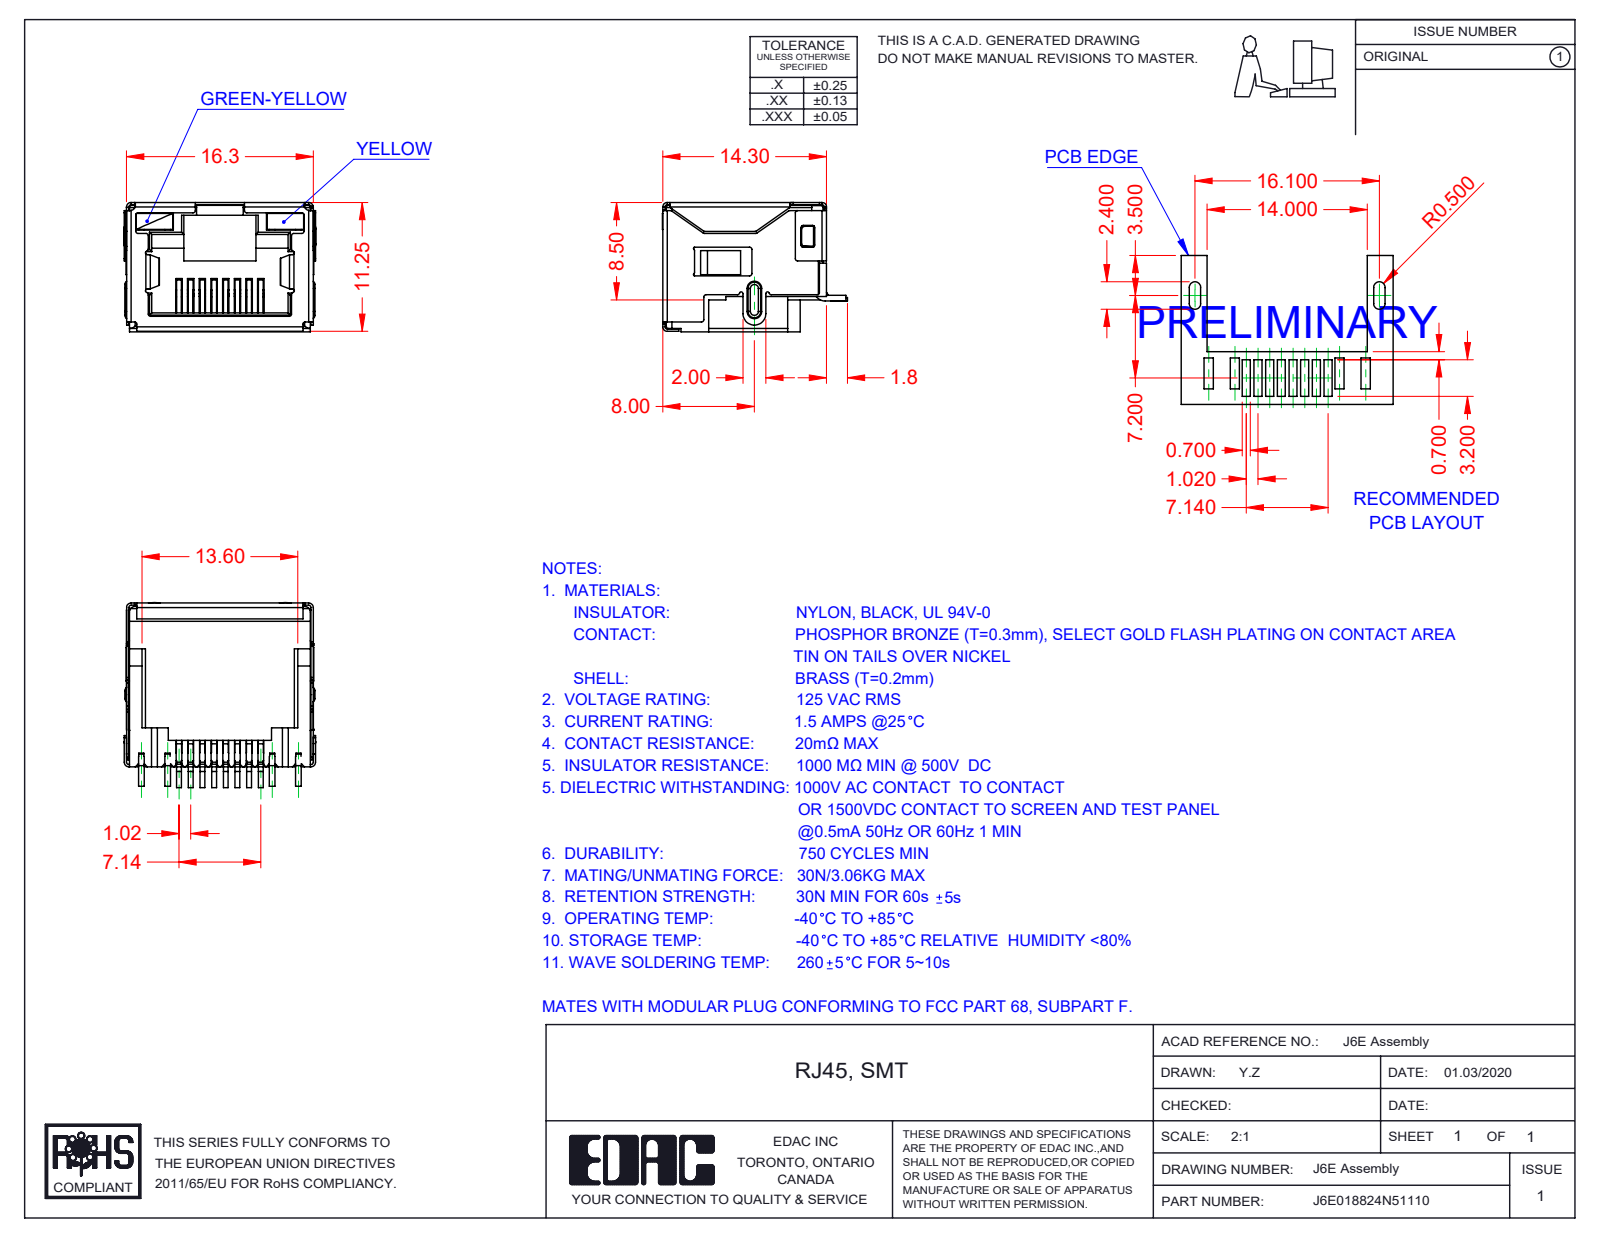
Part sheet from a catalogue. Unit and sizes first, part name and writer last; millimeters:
Units: millimetres
Overall size (bounding box): 16.75 × 16.15 × 11.3
Partial cylindrical surfaces — rounded edges, fillets, slot ends (radius × count): R0.2 ×82, R0.25 ×17, R0.4 ×13, R0.5 ×13, R0.1 ×10, R0.15 ×7, R0.3 ×4, R1 ×3
Main face-to-face distances: 11.05, 16.05, 16.1, 15.85, 11.1, 11.3, 2.4, 0.7, 9.85, 0.49
Volume: 1 109 mm³ · Surface area: 4 045 mm²
Bodies: 12 solids, 1498 faces (1099 planar, 349 cylindrical, 50 other)
Part name (STEP PRODUCT): 6E Contacts; 6E LED RH_1-Yellow; 6E Shield_LED; J6E018824N51110 (+2 more)
STEP written by: SolidWorks 2016 (CONFIG_CONTROL_DESIGN)
